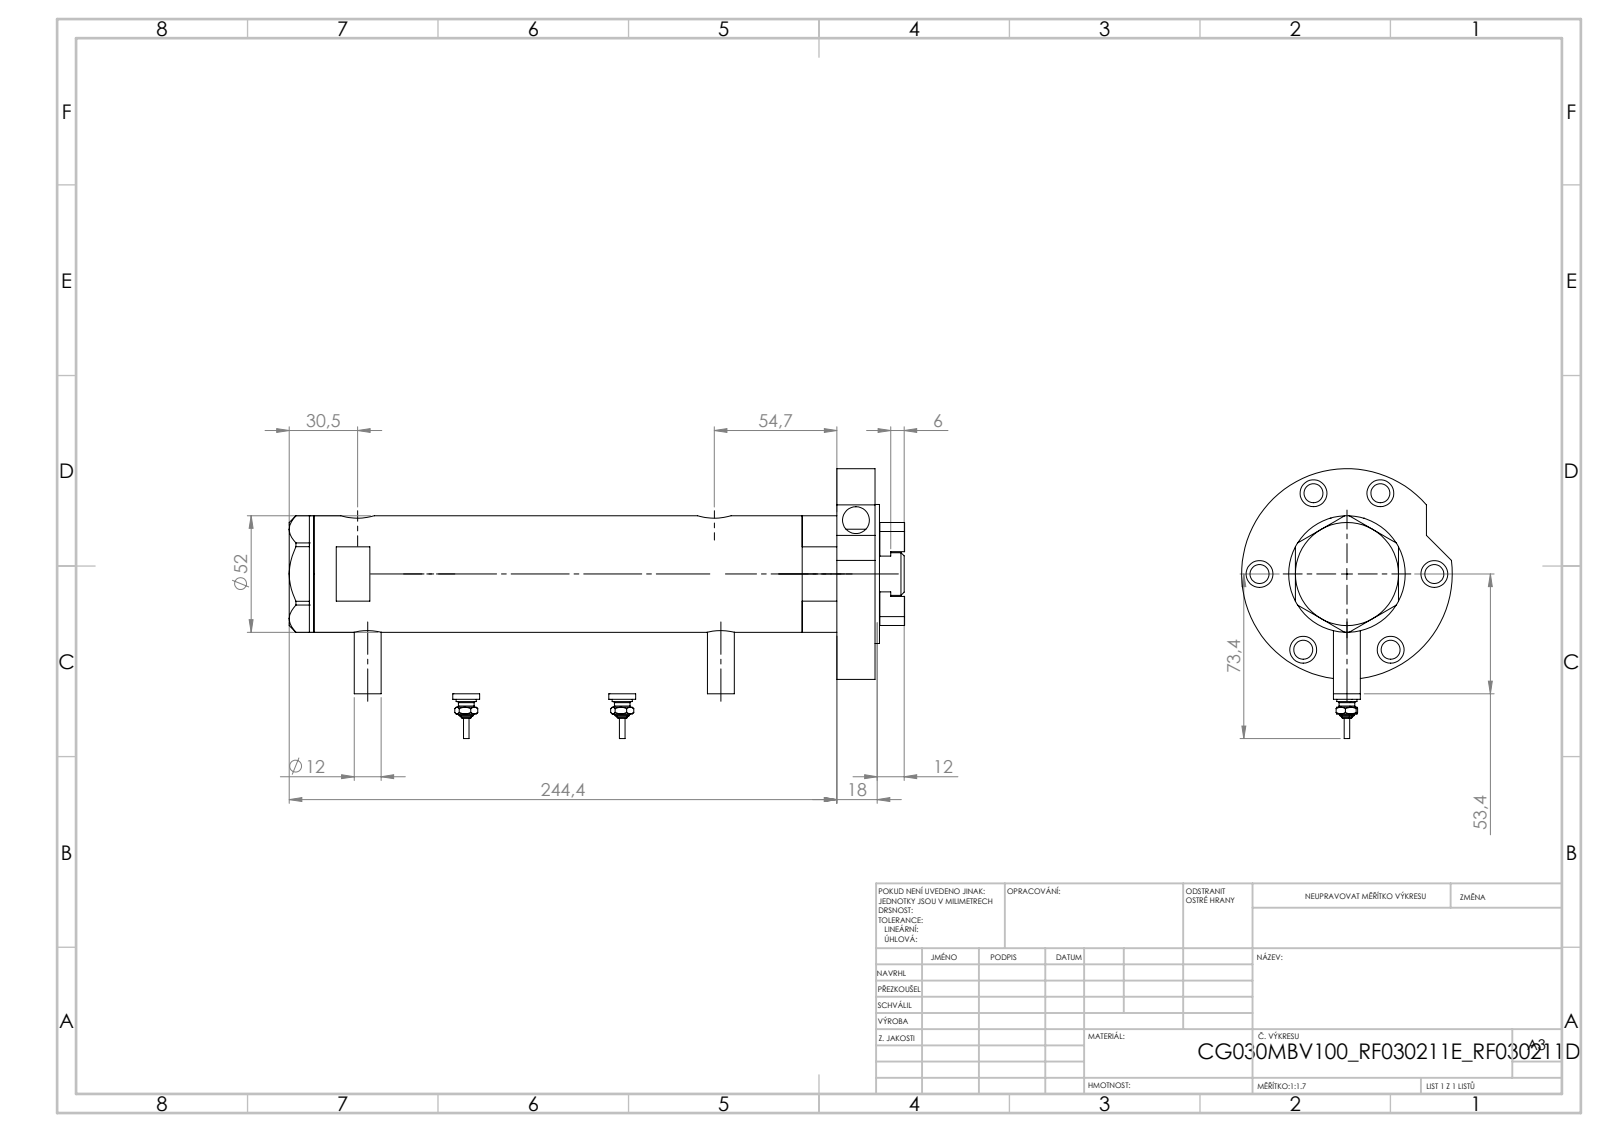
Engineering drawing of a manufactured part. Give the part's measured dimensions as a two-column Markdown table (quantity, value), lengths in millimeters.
| quantity | value |
| --- | --- |
| part name | V270CG_MIDDLE; V270CG_VC; V270CG_RF211E; V270CG_RF211D (+3 more) |
| STEP written by | SolidWorks 2019 (CONFIG_CONTROL_DESIGN) |
| units | millimeters |
| bodies | 9 solids, 330 faces (130 planar, 126 cylindrical, 74 other) |
| overall size | 249.22 × 105.3 × 94 |
| volume | 529 566 mm³ |
| surface area | 126 281 mm² |
| round holes (diameter × count) | 12 × 7, 8.5 × 6, 5.1 × 4, 9 × 4, 5 × 2, 9.73 × 2, 12.5 × 2, 15 × 2, 6.5 × 1, 20 × 1, 21.5 × 1, 30 × 1 |
| round bosses / shafts (diameter × count) | 12 × 3, 9 × 2, 7 × 2, 4.34 × 2, 2.4 × 2, 94 × 1, 62 × 1, 52 × 1 |
| main face-to-face distances | 17, 205.44, 222.44, 2, 51.9, 224.44, 11, 153.54, 68.9, 70.9 |
| hole center spacings | 39, 16.74, 37.57, 46.81, 2.9, 4.5, 10, 22.37 |
